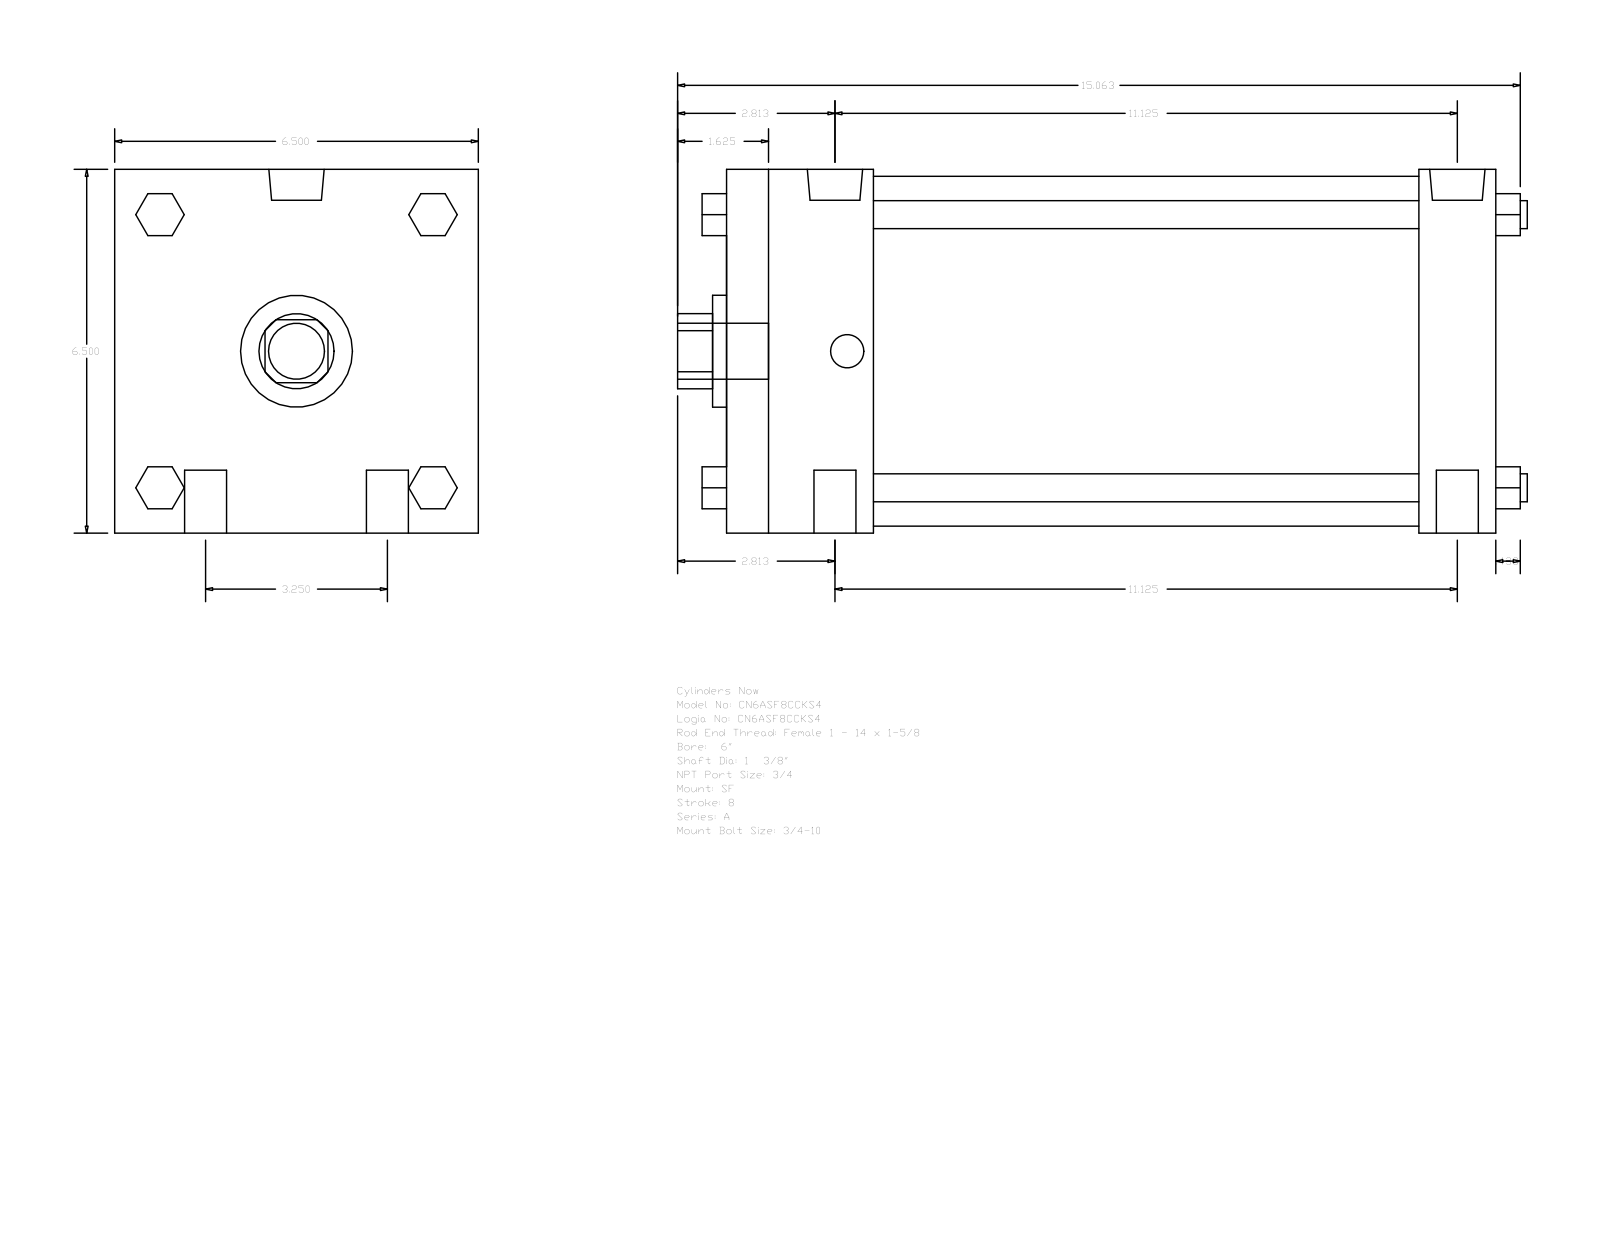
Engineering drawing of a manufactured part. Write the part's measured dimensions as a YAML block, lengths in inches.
part_name: "A_SF__0600_1.375"
step_written_by: "GSSL Pune (CONFIG_CONTROL_DESIGN)"
units: inches
bodies: {solids: 0, faces: 124, planar: 94, cylindrical: 30, other: 0}
overall_size: [15.187, 6.5, 6.5]
round_holes:
  - {diameter: 1.375, count: 1}
  - {diameter: 2, count: 1}
  - {diameter: 6.25, count: 1}
round_bosses_or_shafts:
  - {diameter: 0.75, count: 4}
  - {diameter: 0.5, count: 4}
  - {diameter: 0.989, count: 2}
  - {diameter: 0.594, count: 2}
  - {diameter: 1, count: 1}
partial_cylinders:
  - {radius: 0.672, count: 1}
face_to_face_distances: [6.5, 13.75, 12.375, 1.375, 2.625, 9.75, 11.125, 0.75, 2.44, 4.226]
